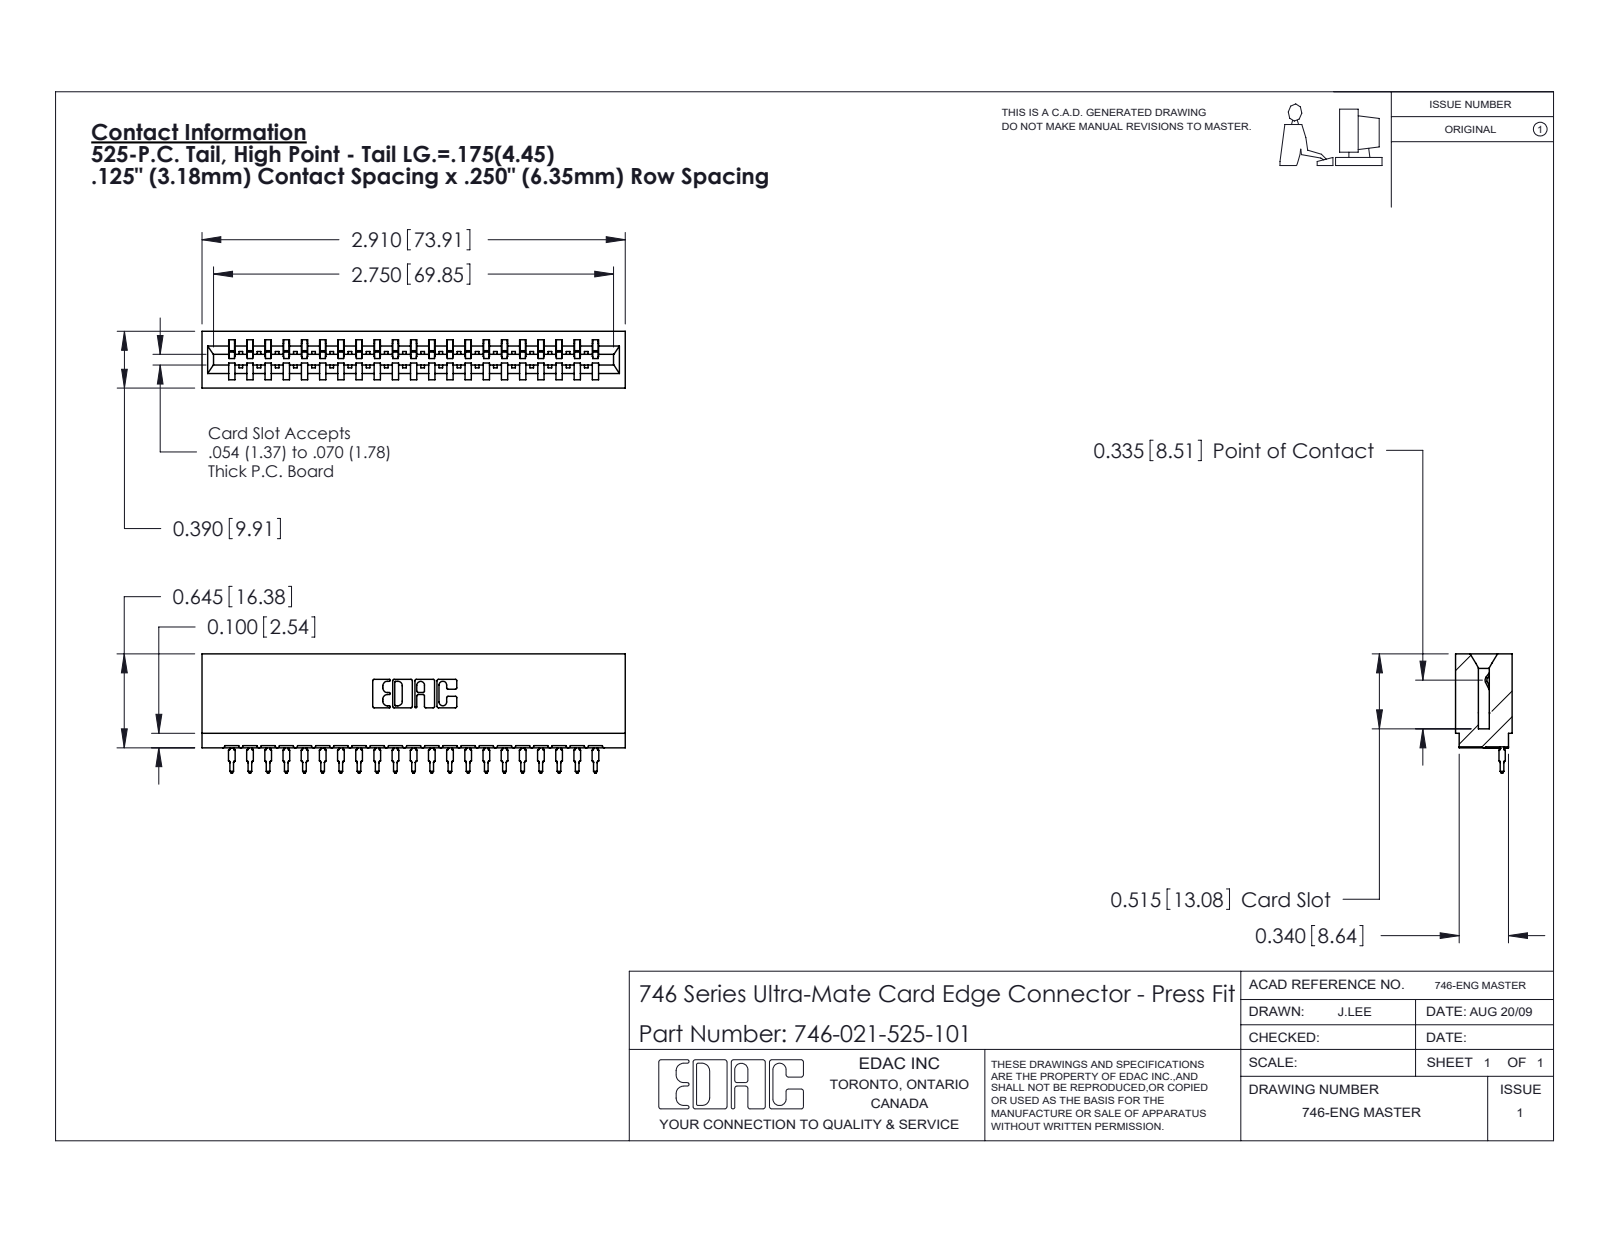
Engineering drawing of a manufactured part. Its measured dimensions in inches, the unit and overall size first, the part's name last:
Units: inches
Overall size (bounding box): 2.91 × 0.819 × 0.39
Partial cylindrical surfaces — rounded edges, fillets, slot ends (radius × count): R0.021 ×42, R0.01 ×22, R0.015 ×22, R0.007 ×6, R0.031 ×6, R0.005 ×4, R0.011 ×4, R0.026 ×3
Main face-to-face distances: 0.25, 0.333, 0.057, 0.39, 0.5, 0.042, 0.125, 0.025, 0.307, 0.375
Volume: 0.478 in³ · Surface area: 17.31 in²
Bodies: 22 solids, 2365 faces (1378 planar, 441 cylindrical, 546 other)
Part name (STEP PRODUCT): 746 Part_.515 Slot Depth - 01; 746-021-525-101; 746-292-001_525
STEP written by: SolidWorks 2020 (CONFIG_CONTROL_DESIGN)
